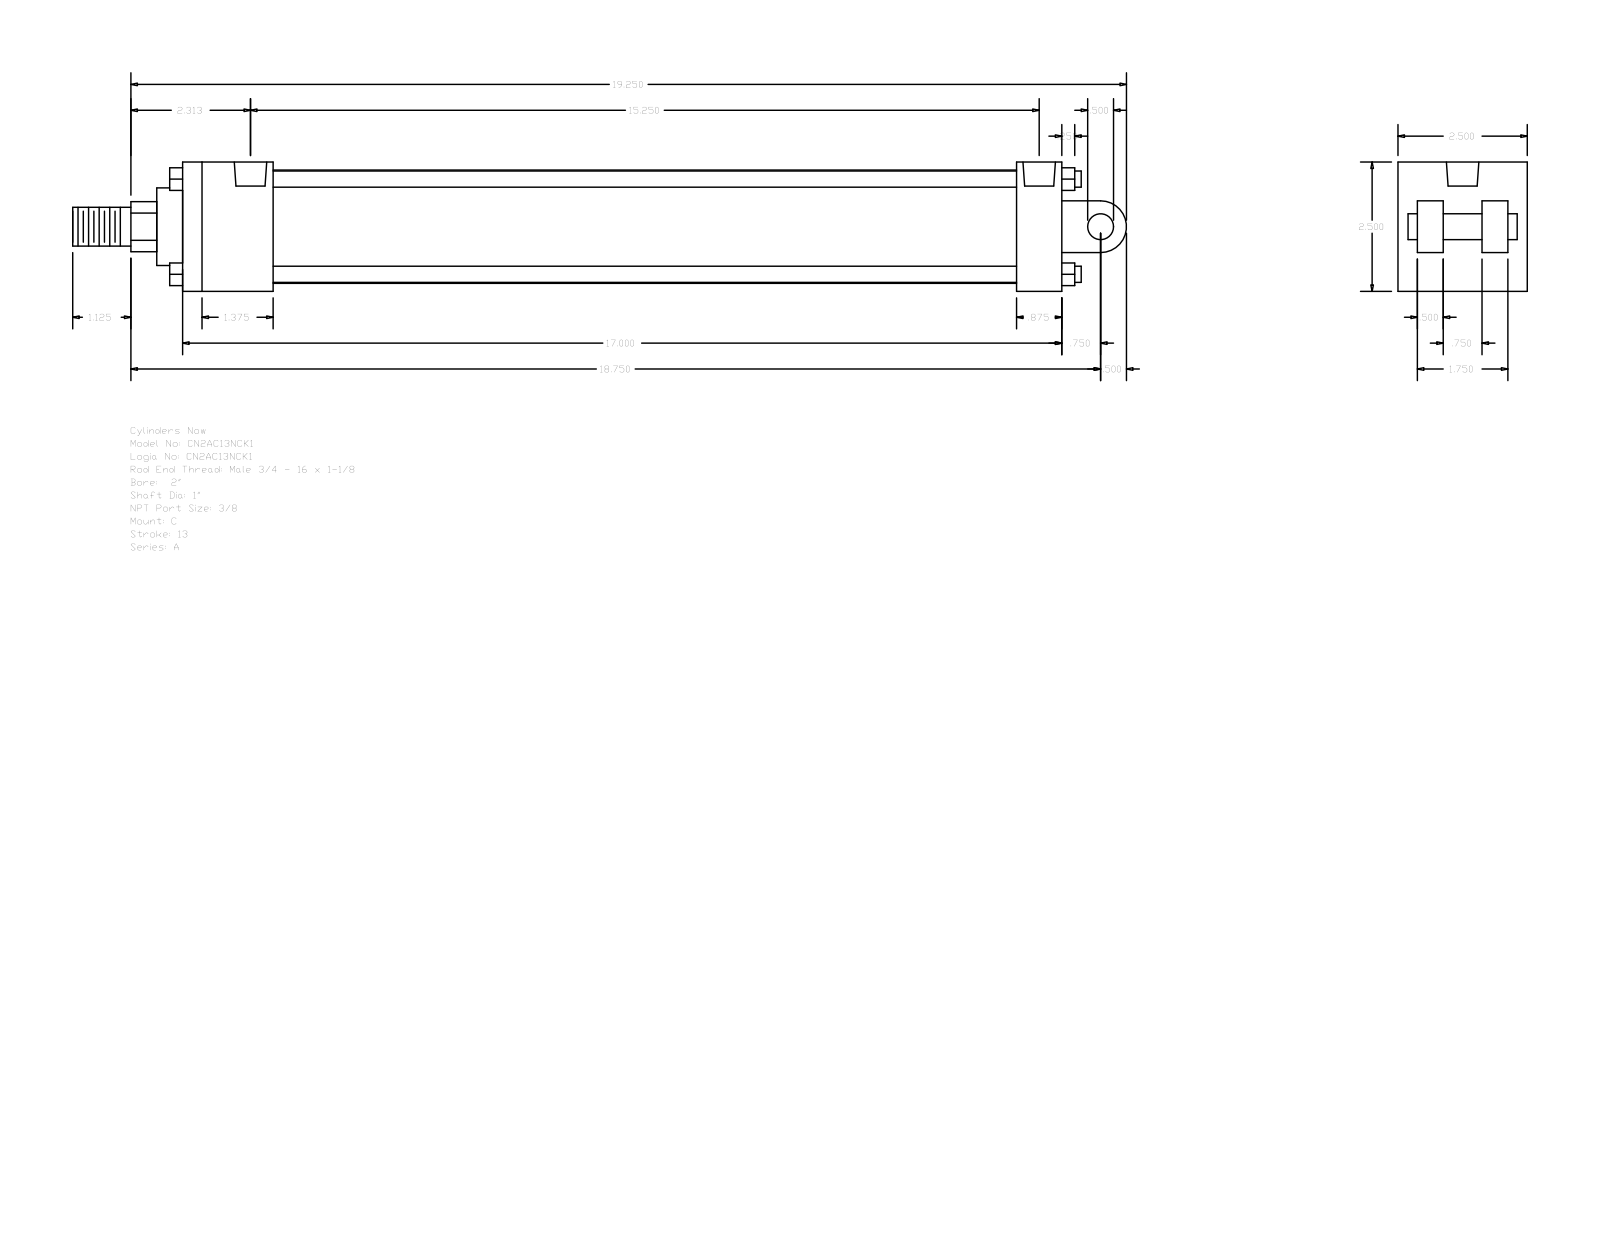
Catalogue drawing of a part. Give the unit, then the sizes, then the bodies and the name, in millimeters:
Units: millimetres
Overall size (bounding box): 517.52 × 63.5 × 63.5
Round holes (diameter × count): ⌀5.56 ×4, ⌀15.93 ×2
Round bosses / shafts (diameter × count): ⌀7.94 ×4, ⌀55.63 ×1, ⌀38.1 ×1, ⌀25.4 ×1, ⌀19.05 ×1, ⌀12.7 ×1
Partial cylindrical surfaces — rounded edges, fillets, slot ends (radius × count): R12.29 ×1, R12.7 ×1
Main face-to-face distances: 63.5, 22.22, 431.8, 44.45, 12.7, 387.35, 409.58, 365.13, 9.52, 41.28
Hole centre spacings: 381.78, 1.59, 3.98, 383.37, 385.76, 387.35
Bodies: 0 solids, 135 faces (102 planar, 33 cylindrical, 0 other)
Part name (STEP PRODUCT): A_C__0200_1
STEP written by: GSSL Pune (CONFIG_CONTROL_DESIGN)
